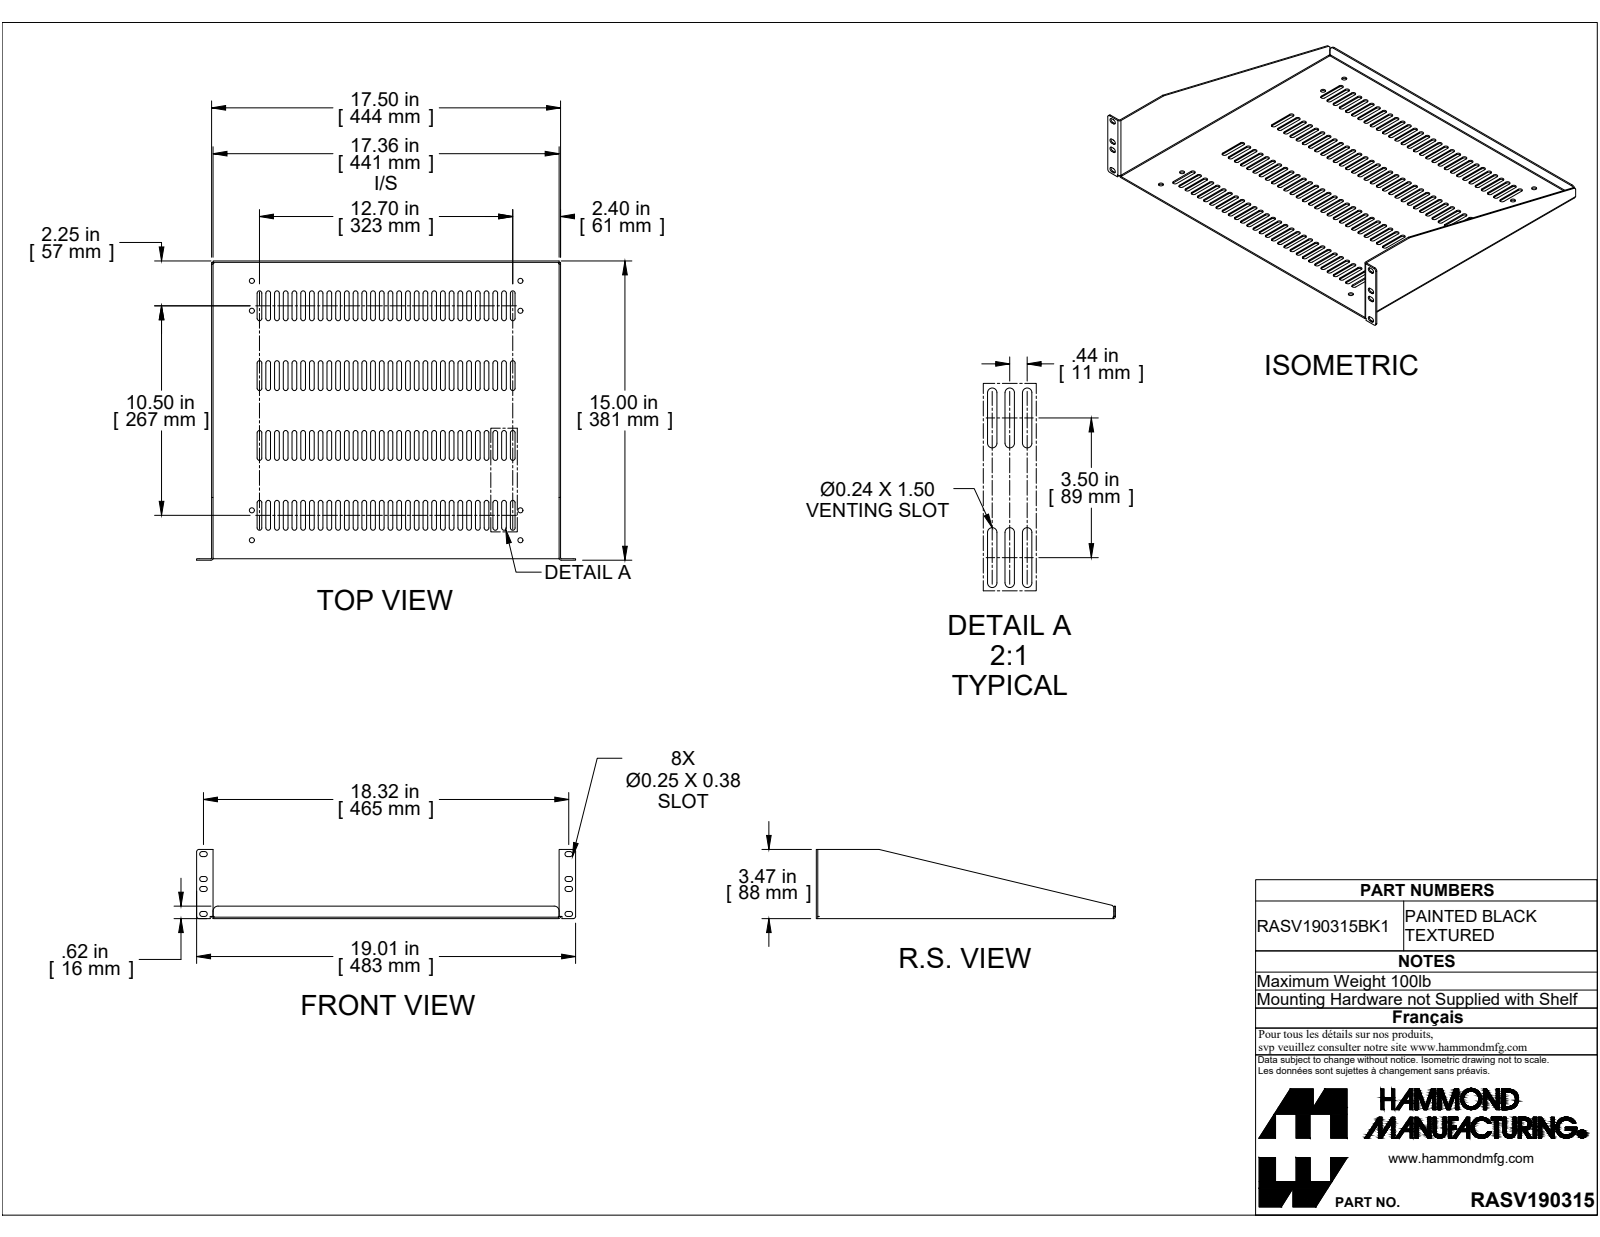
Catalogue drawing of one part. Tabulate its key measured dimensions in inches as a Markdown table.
| quantity | value |
| --- | --- |
| part name | RASV190315BK1 |
| STEP written by | SolidWorks 2019 (CONFIG_CONTROL_DESIGN) |
| units | inches |
| bodies | 1 solid, 584 faces (296 planar, 284 cylindrical, 4 other) |
| overall size | 19.006 × 15 × 3.468 |
| volume | 21.64 in³ |
| surface area | 635.9 in² |
| round holes (diameter × count) | 0.25 × 8 |
| partial cylindrical surfaces (radius × count) | 0.118 × 232, 0.125 × 20, 0.117 × 8, 0.036 × 5, 0.108 × 5, 0.055 × 3, 0.25 × 2 |
| main face-to-face distances | 0.072, 17.428, 17.356, 17.5, 14.856, 14.928, 0.876, 0.072, 14.928, 15 |
| hole center spacings | 1.5, 11.5, 13.468, 13.551, 17.709, 10, 13, 16.774 |
